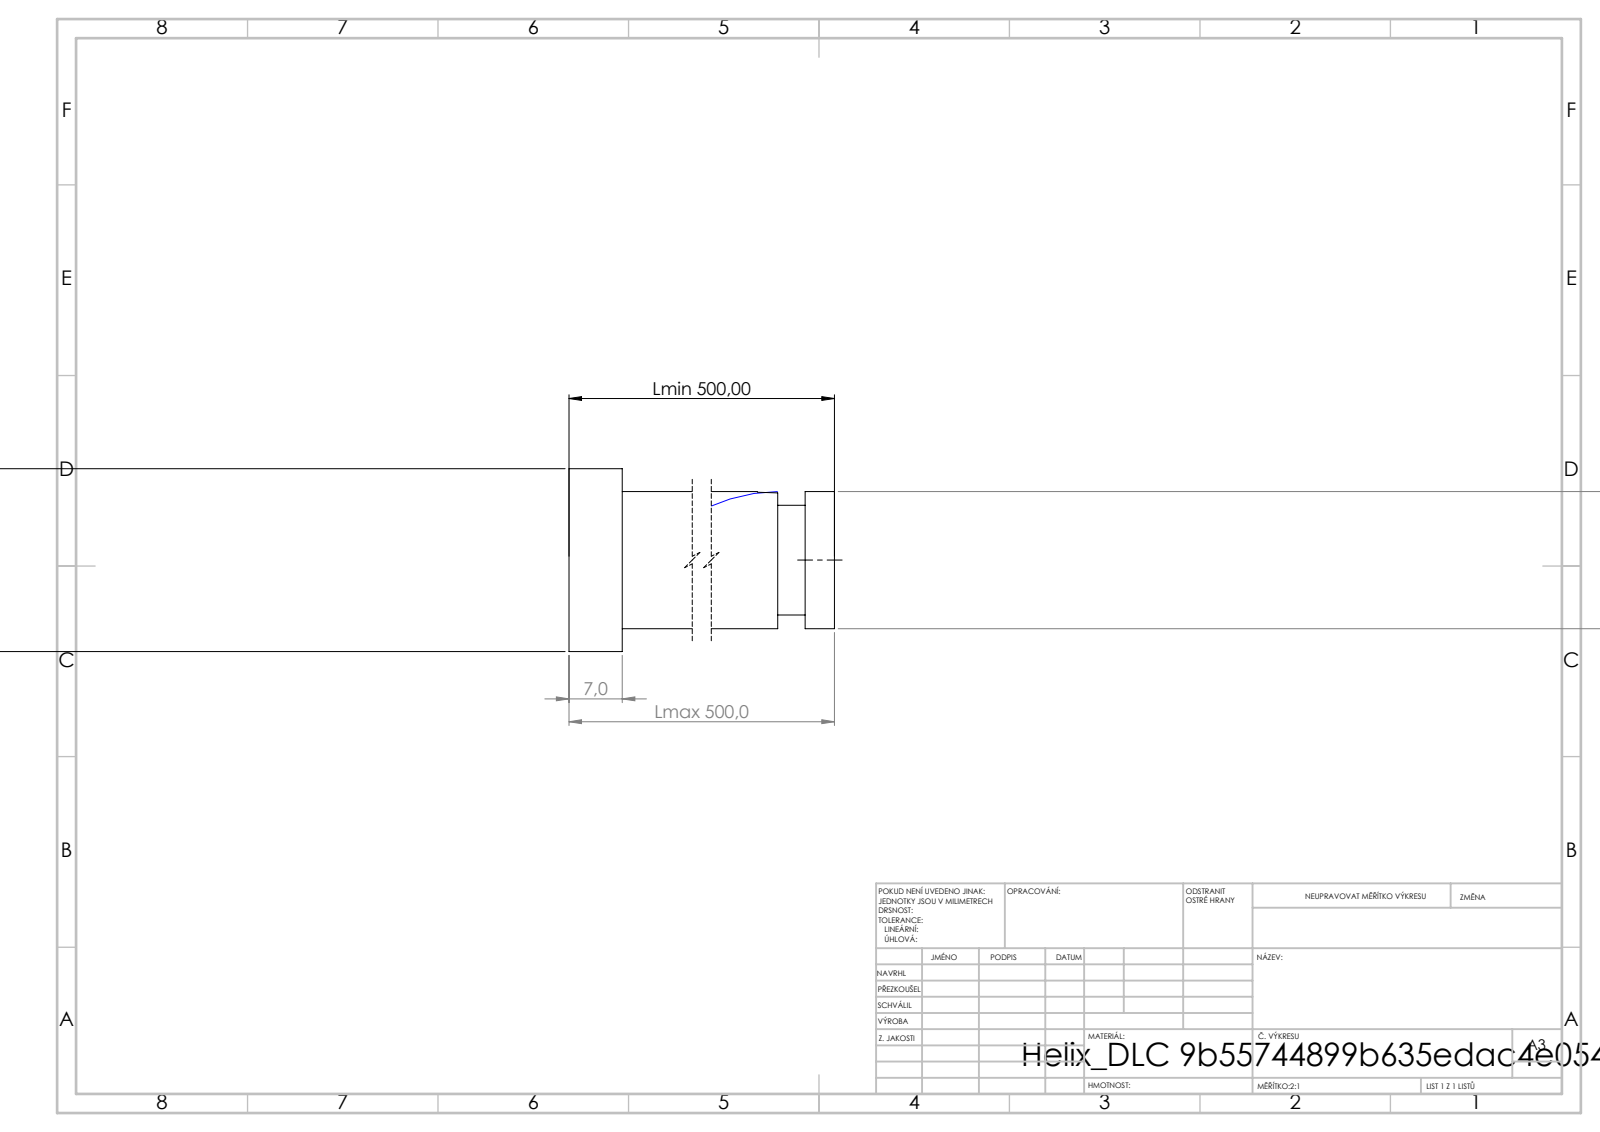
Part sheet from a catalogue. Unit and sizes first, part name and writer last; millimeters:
Units: millimetres
Overall size (bounding box): 500 × 24 × 24
Round bosses / shafts (diameter × count): ⌀24 ×1, ⌀18 ×1, ⌀14.4 ×1
Main face-to-face distances: 500, 7, 493, 496.16, 489.16, 3.84, 492.56, 485.56, 3.6, 7.44
Volume: 127 072 mm³ · Surface area: 30 008 mm²
Bodies: 1 solid, 21 faces (6 planar, 14 cylindrical, 1 other)
STEP written by: SolidWorks 2019 (CONFIG_CONTROL_DESIGN)
